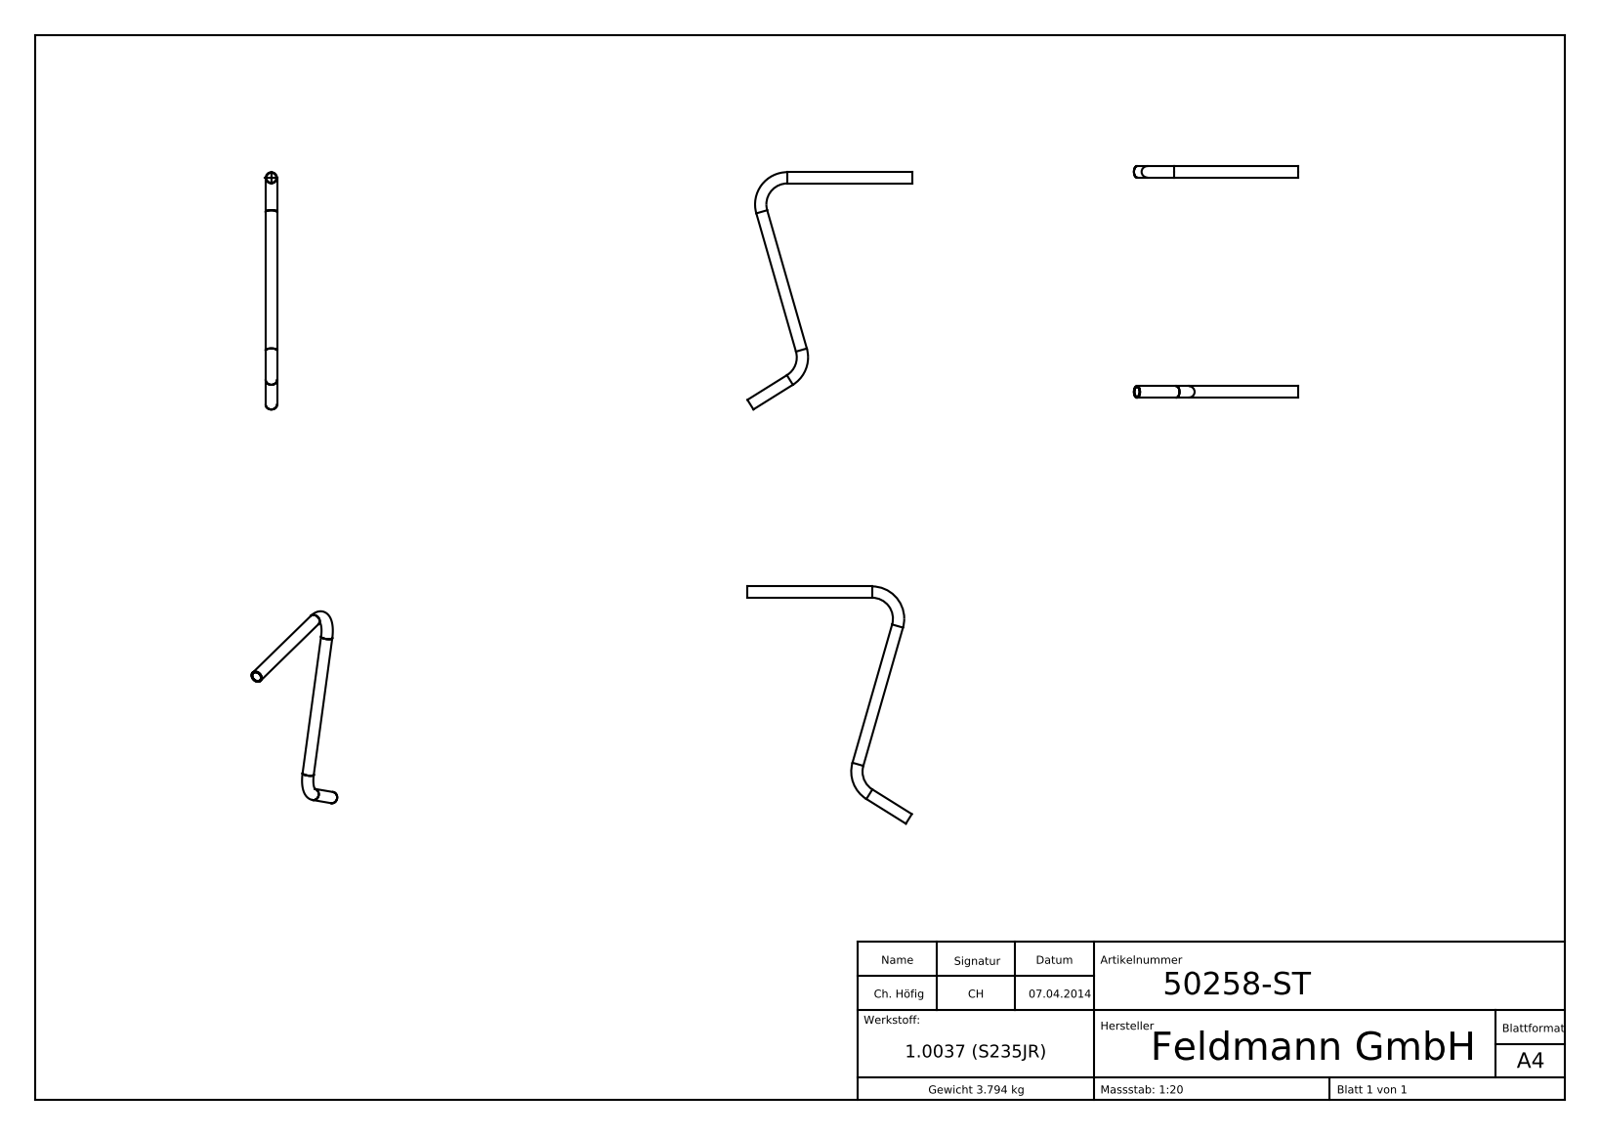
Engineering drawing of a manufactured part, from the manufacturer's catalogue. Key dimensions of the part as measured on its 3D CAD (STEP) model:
Part name (STEP PRODUCT): 50258-ST
STEP written by: SolidWorks 2015 (CONFIG_CONTROL_DESIGN)
Units: millimetres
Bodies: 1 solid, 249 faces (110 planar, 12 cylindrical, 127 other)
Overall size (bounding box): 890.68 × 617.07 × 42.4
Volume: 486 349 mm³ · Surface area: 374 802 mm²
Round holes (diameter × count): ⌀37.2 ×3
Round bosses / shafts (diameter × count): ⌀42.4 ×3
Main face-to-face distances: 0.5, 0.43, 0.58, 0.53, 1.07, 0.68, 0.54, 1.17, 0.97, 0.33
